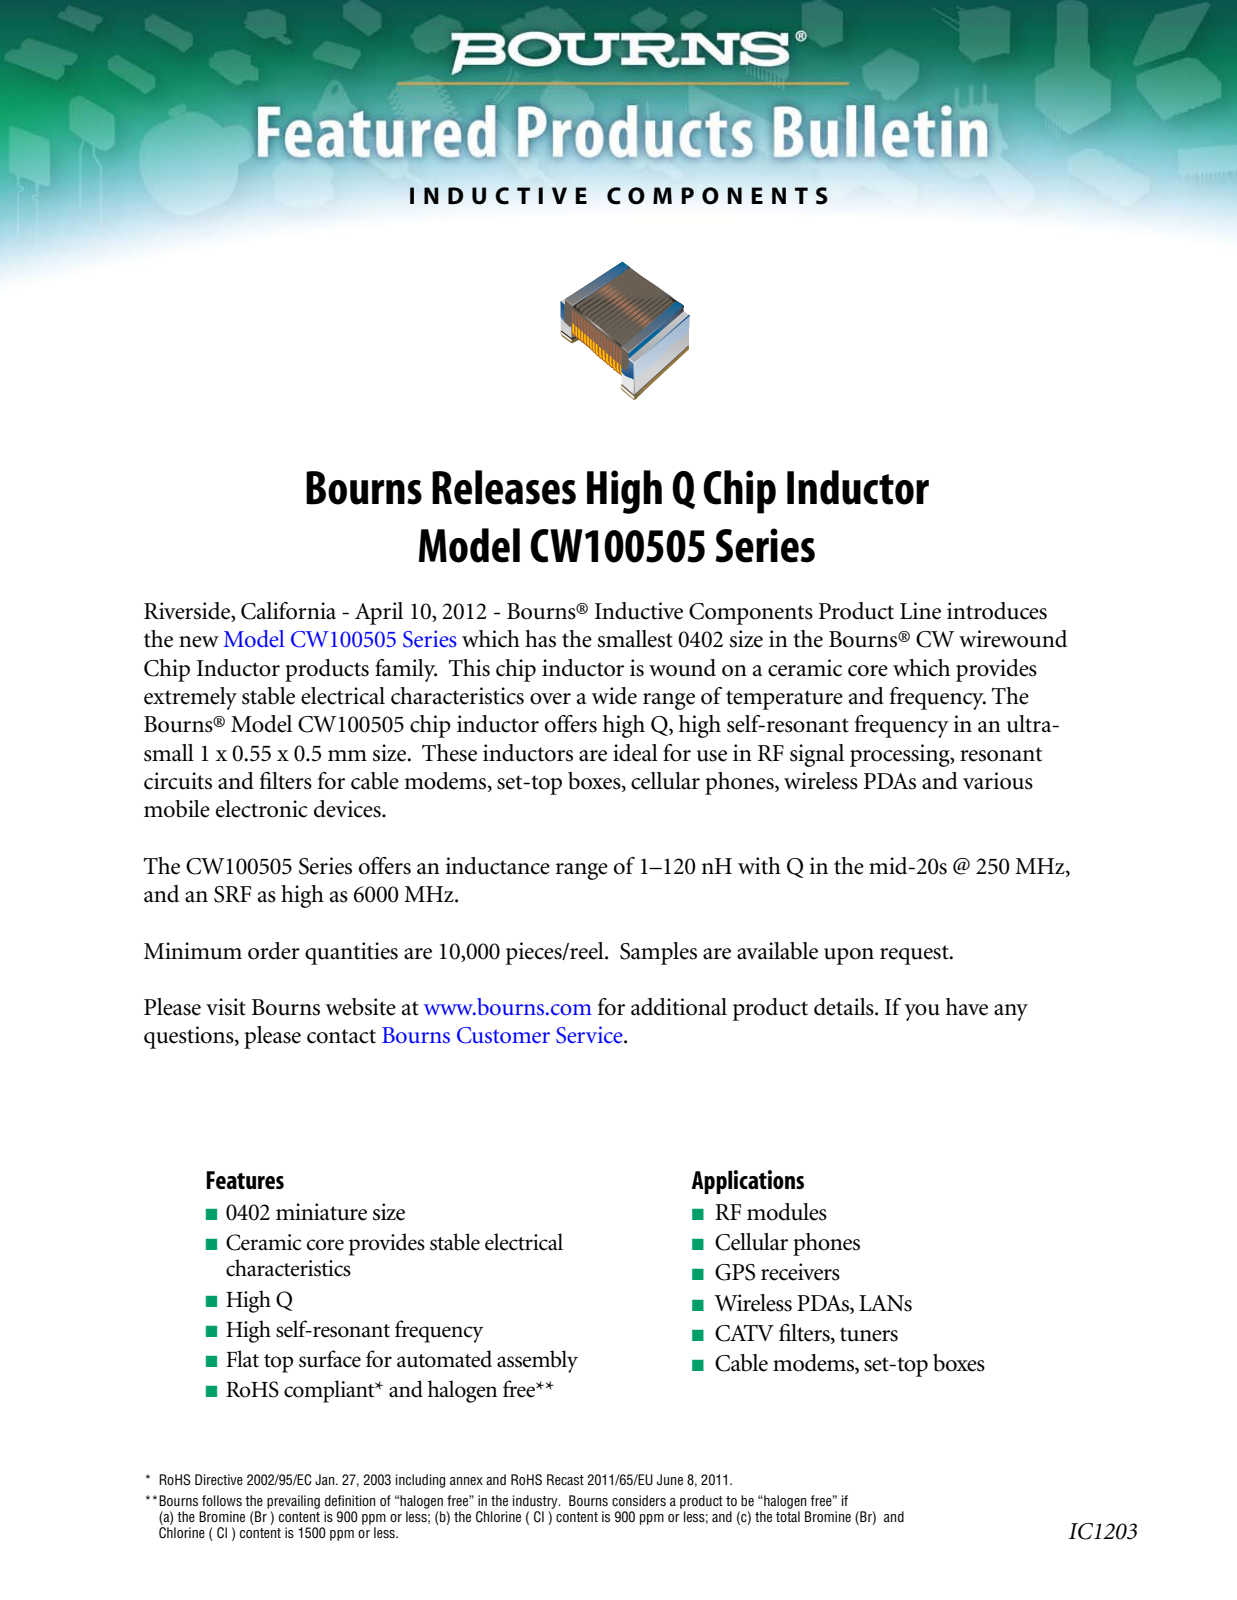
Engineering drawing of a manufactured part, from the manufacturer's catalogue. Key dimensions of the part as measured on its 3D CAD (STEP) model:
Part name (STEP PRODUCT): CW100505
STEP written by: PRO/ENGINEER BY PARAMETRIC TECHNOLOGY CORPORATION, 2010100 (CONFIG_CONTROL_DESIGN)
Units: millimetres
Bodies: 1 solid, 315 faces (135 planar, 120 cylindrical, 60 other)
Overall size (bounding box): 1 × 0.55 × 0.5
Volume: 0.237 mm³ · Surface area: 3 mm²
Main face-to-face distances: 0.56, 0.51, 0.5, 0.99, 1, 0.43, 0.46, 0.98, 0.79, 0.78
